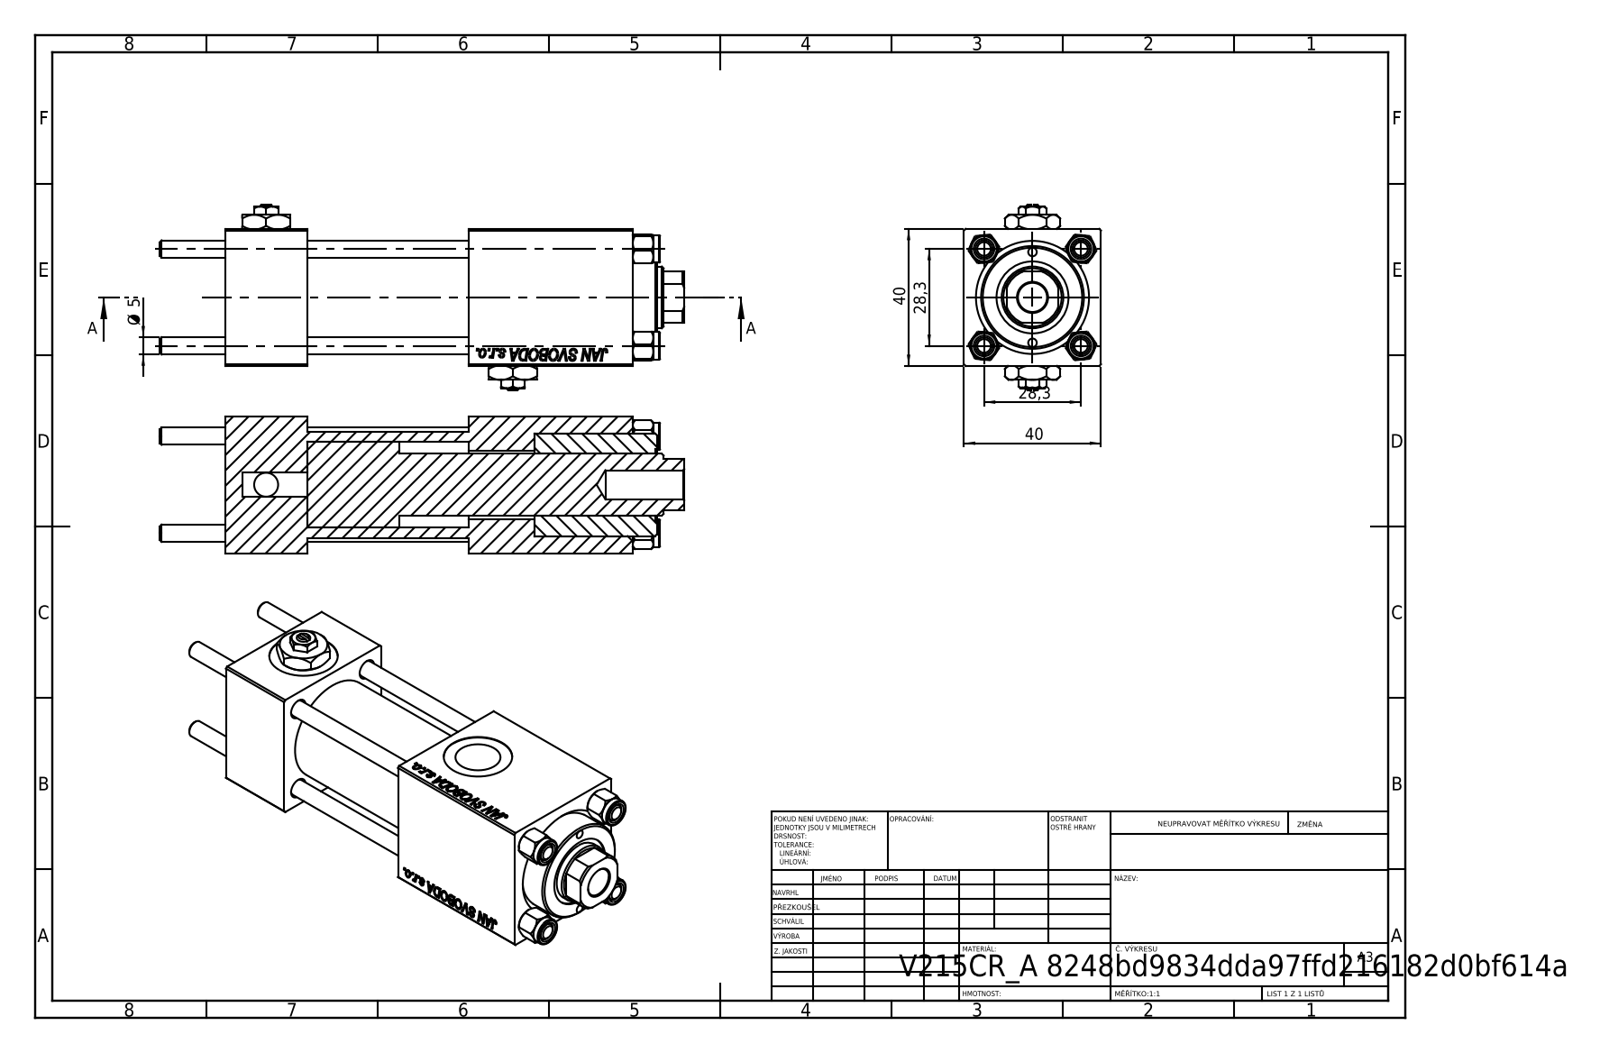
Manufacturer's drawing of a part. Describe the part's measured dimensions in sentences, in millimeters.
The part is named "NUT_M5; CR025_012_A_0_G_A_G_M_020_+#_##_TYCINKA; V215_VC_A; V215CR_VCP (+2 more)". Its 3-D file was written by "SolidWorks 2019 (CONFIG_CONTROL_DESIGN)". It is 13 solids with 1235 faces: 565 planar, 92 cylindrical and 578 other. Overall it measures 153 by 54 by 40 millimeters. Its volume is 150 909 cubic millimeters and its surface area 63 103 square millimeters. Round holes: 4 of diameter 5, 3 of diameter 20, 2 of diameter 2.5, 2 of diameter 7, 2 of diameter 13.16, 1 of diameter 8.5, 1 of diameter 18, 1 of diameter 21, 1 of diameter 25, 1 of diameter 30. Round bosses or shafts: 4 of diameter 8, 1 of diameter 31. Partial cylindrical surfaces (rounded edges, fillets, slot ends): 1 of radius 8.5. The main face-to-face distances are 40, 24, 39.8, 47, 71, 90.3, 66.3, 19.3, 95, 119. The hole center spacings are 14.18, 20.01, 28.3, 30.84, 13.25, 40.02, 26.5, 72.
